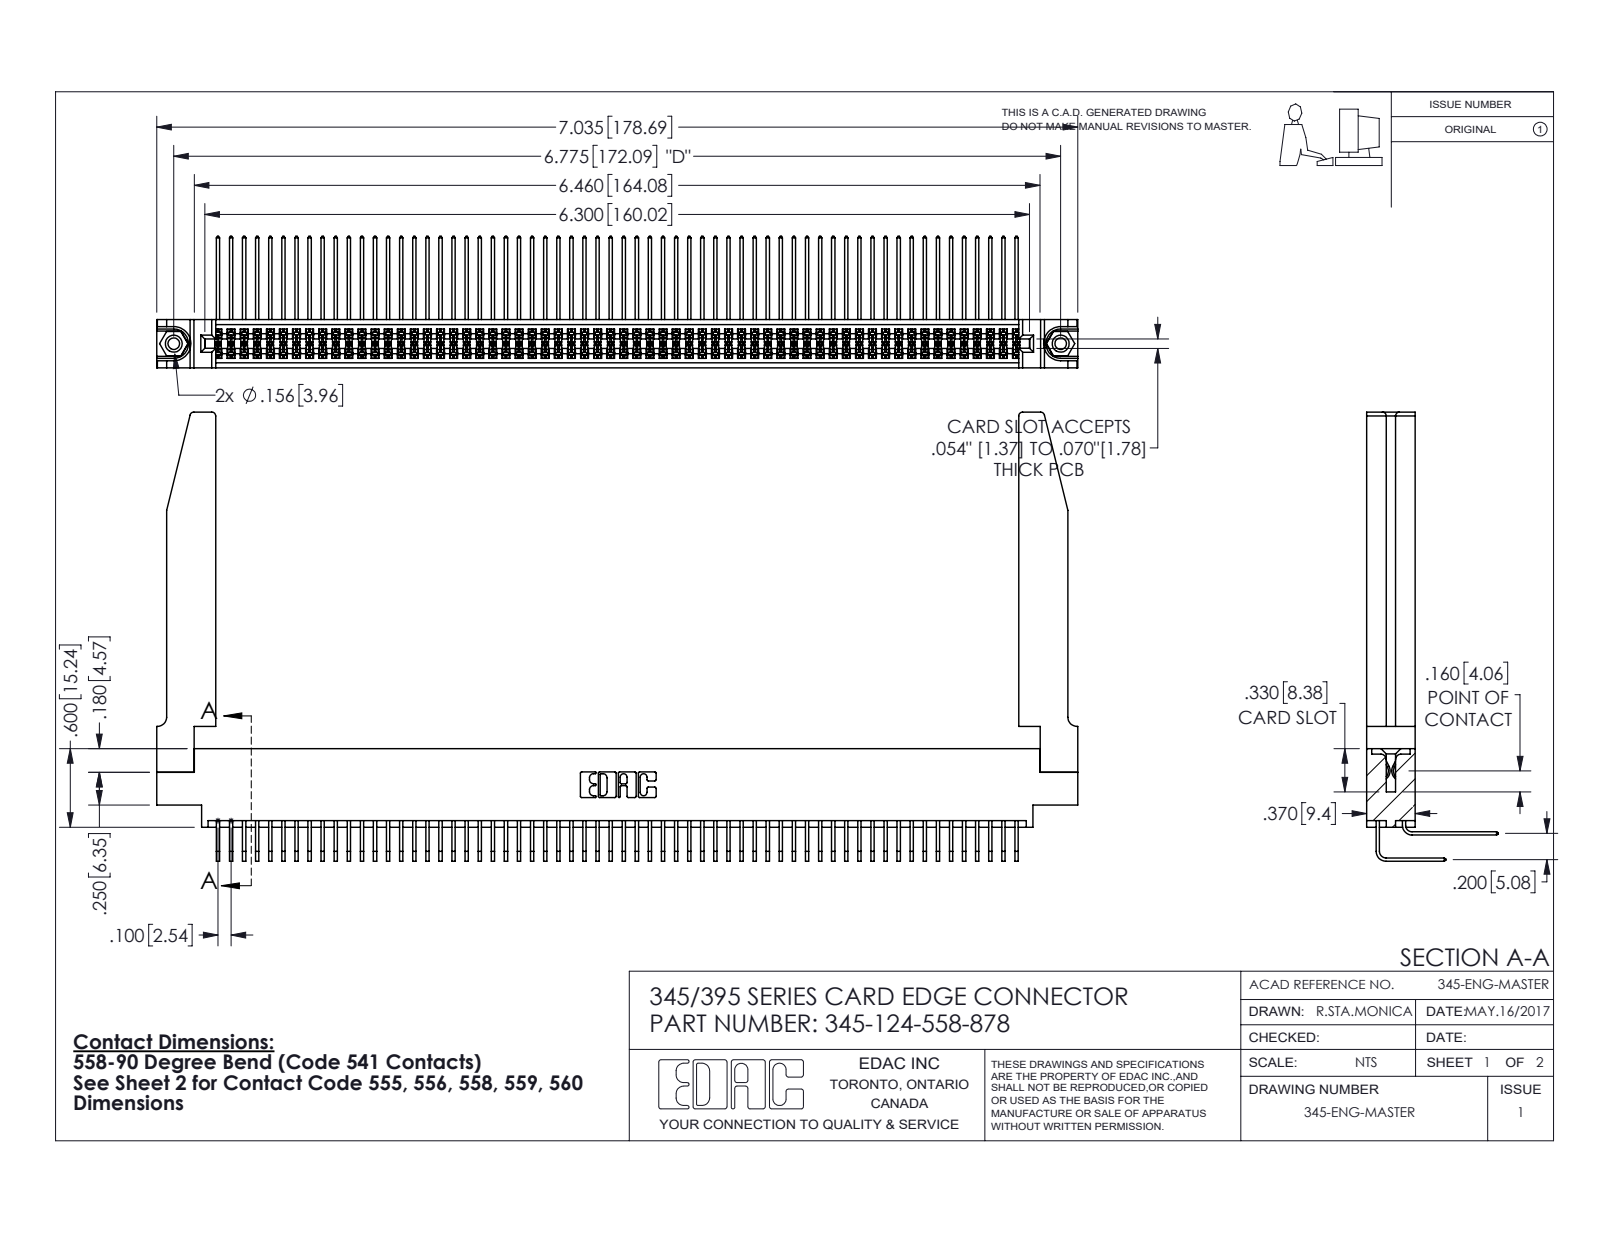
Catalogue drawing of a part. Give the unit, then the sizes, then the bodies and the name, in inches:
Units: inches
Overall size (bounding box): 7.036 × 3.429 × 1.005
Round holes (diameter × count): ⌀0.089 ×2, ⌀0.125 ×2, ⌀0.156 ×2, ⌀0.064 ×1
Round bosses / shafts (diameter × count): ⌀0.155 ×2
Partial cylindrical surfaces — rounded edges, fillets, slot ends (radius × count): R0.006 ×248, R0.01 ×22, R0.03 ×8, R0.007 ×6, R0.031 ×6, R0.026 ×3, R0.014 ×2, R0.019 ×2
Main face-to-face distances: 0.072, 0.298, 0.37, 0.2, 0.098, 0.272, 0.025, 0.225, 0.175, 0.025
Hole centre spacings: 0.27, 6.539, 6.775
Volume: 1.582 in³ · Surface area: 58.22 in²
Bodies: 129 solids, 6812 faces (4566 planar, 2194 cylindrical, 52 other)
Part name (STEP PRODUCT): 345-250-001_345-250-001-102; 345-292-001_558 559 Tail - 1; 345 Part_0.170 Offset - 0.156 Dia-TH; 345-220-078_345-220-078 (+2 more)
STEP written by: SolidWorks 2016 (CONFIG_CONTROL_DESIGN)
